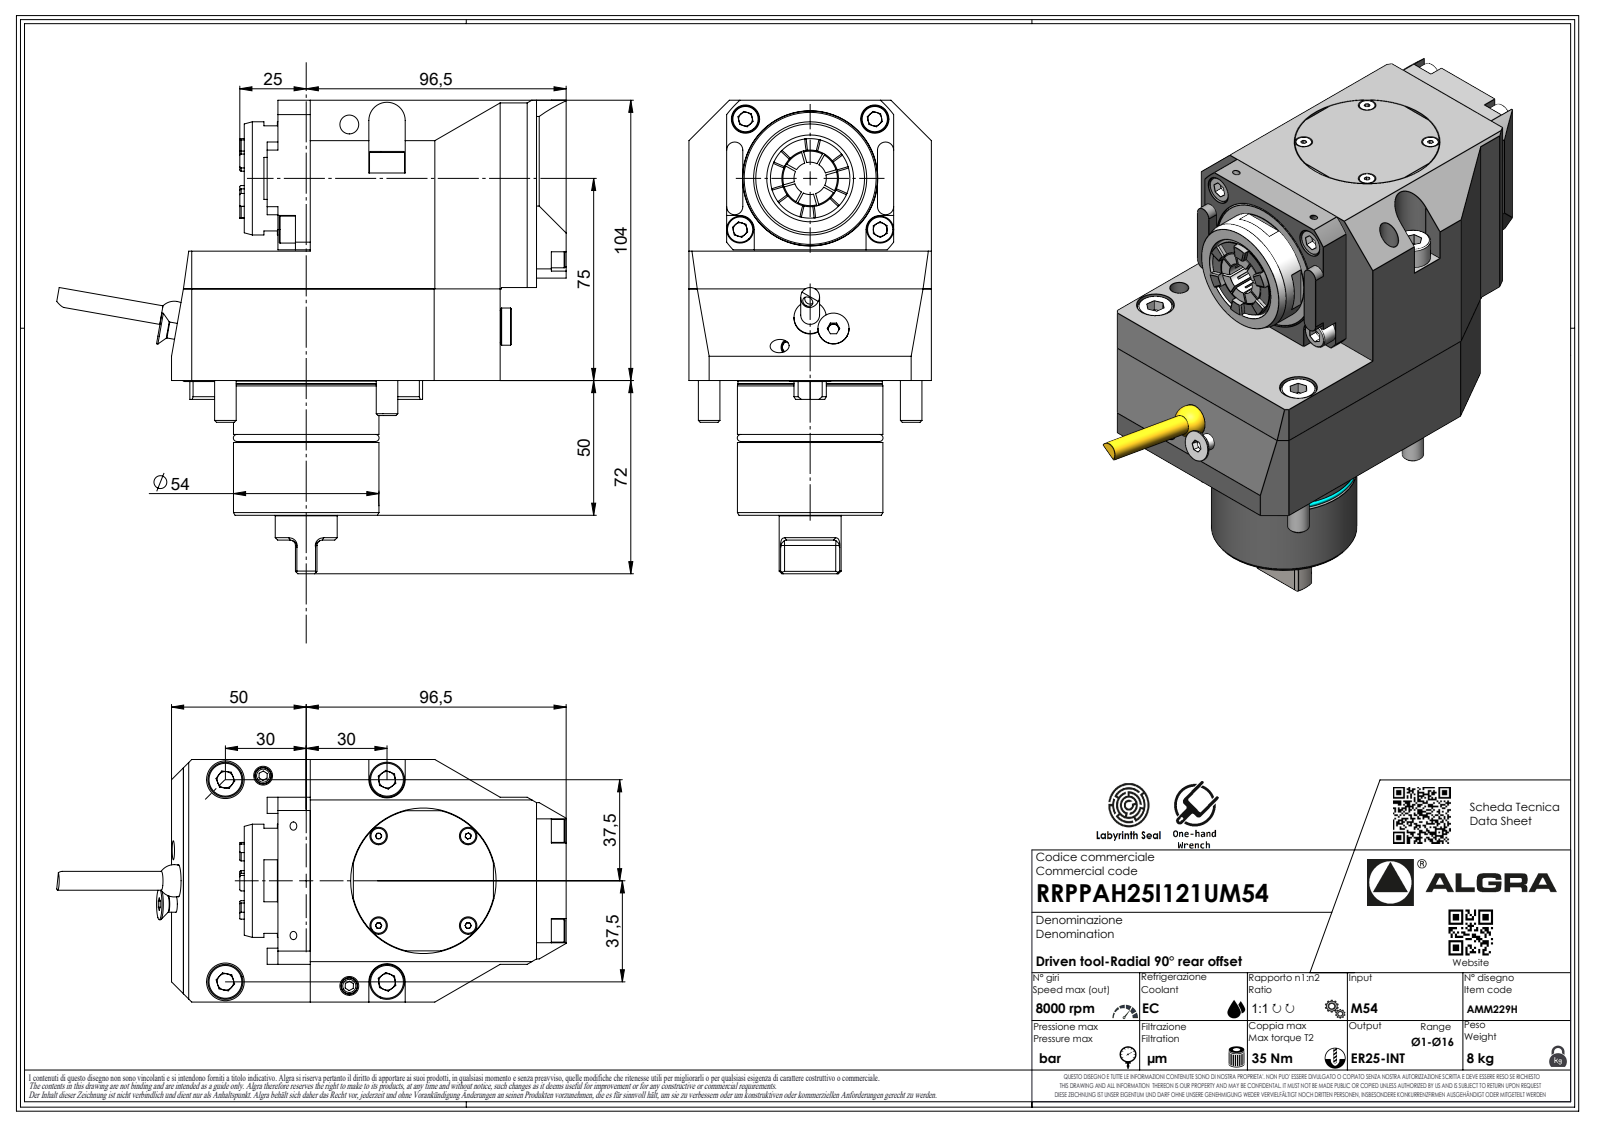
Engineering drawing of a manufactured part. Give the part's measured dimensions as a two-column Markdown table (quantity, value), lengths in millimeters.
| quantity | value |
| --- | --- |
| part name | RRPPAH25I121UM54 |
| STEP written by | SolidWorks 2023 (AUTOMOTIVE_DESIGN) |
| units | millimeters |
| bodies | 1 solid, 574 faces (375 planar, 98 cylindrical, 101 other) |
| overall size | 189.12 × 175.7 × 90 |
| volume | 1 091 000 mm³ |
| surface area | 80 721 mm² |
| round holes (diameter × count) | 2.1 × 1, 4 × 1 |
| round bosses / shafts (diameter × count) | 8 × 4, 13 × 2, 54 × 1, 53.6 × 1, 49.9 × 1, 42 × 1, 23 × 1, 7 × 1 |
| partial cylindrical surfaces (radius × count) | 35 × 10, 0.33 × 7, 0.52 × 7, 2 × 7, 3.7 × 7, 3 × 4, 4.5 × 4, 5.25 × 2 |
| main face-to-face distances | 104, 90, 56, 48, 24.5, 14, 76, 95, 50, 98 |
